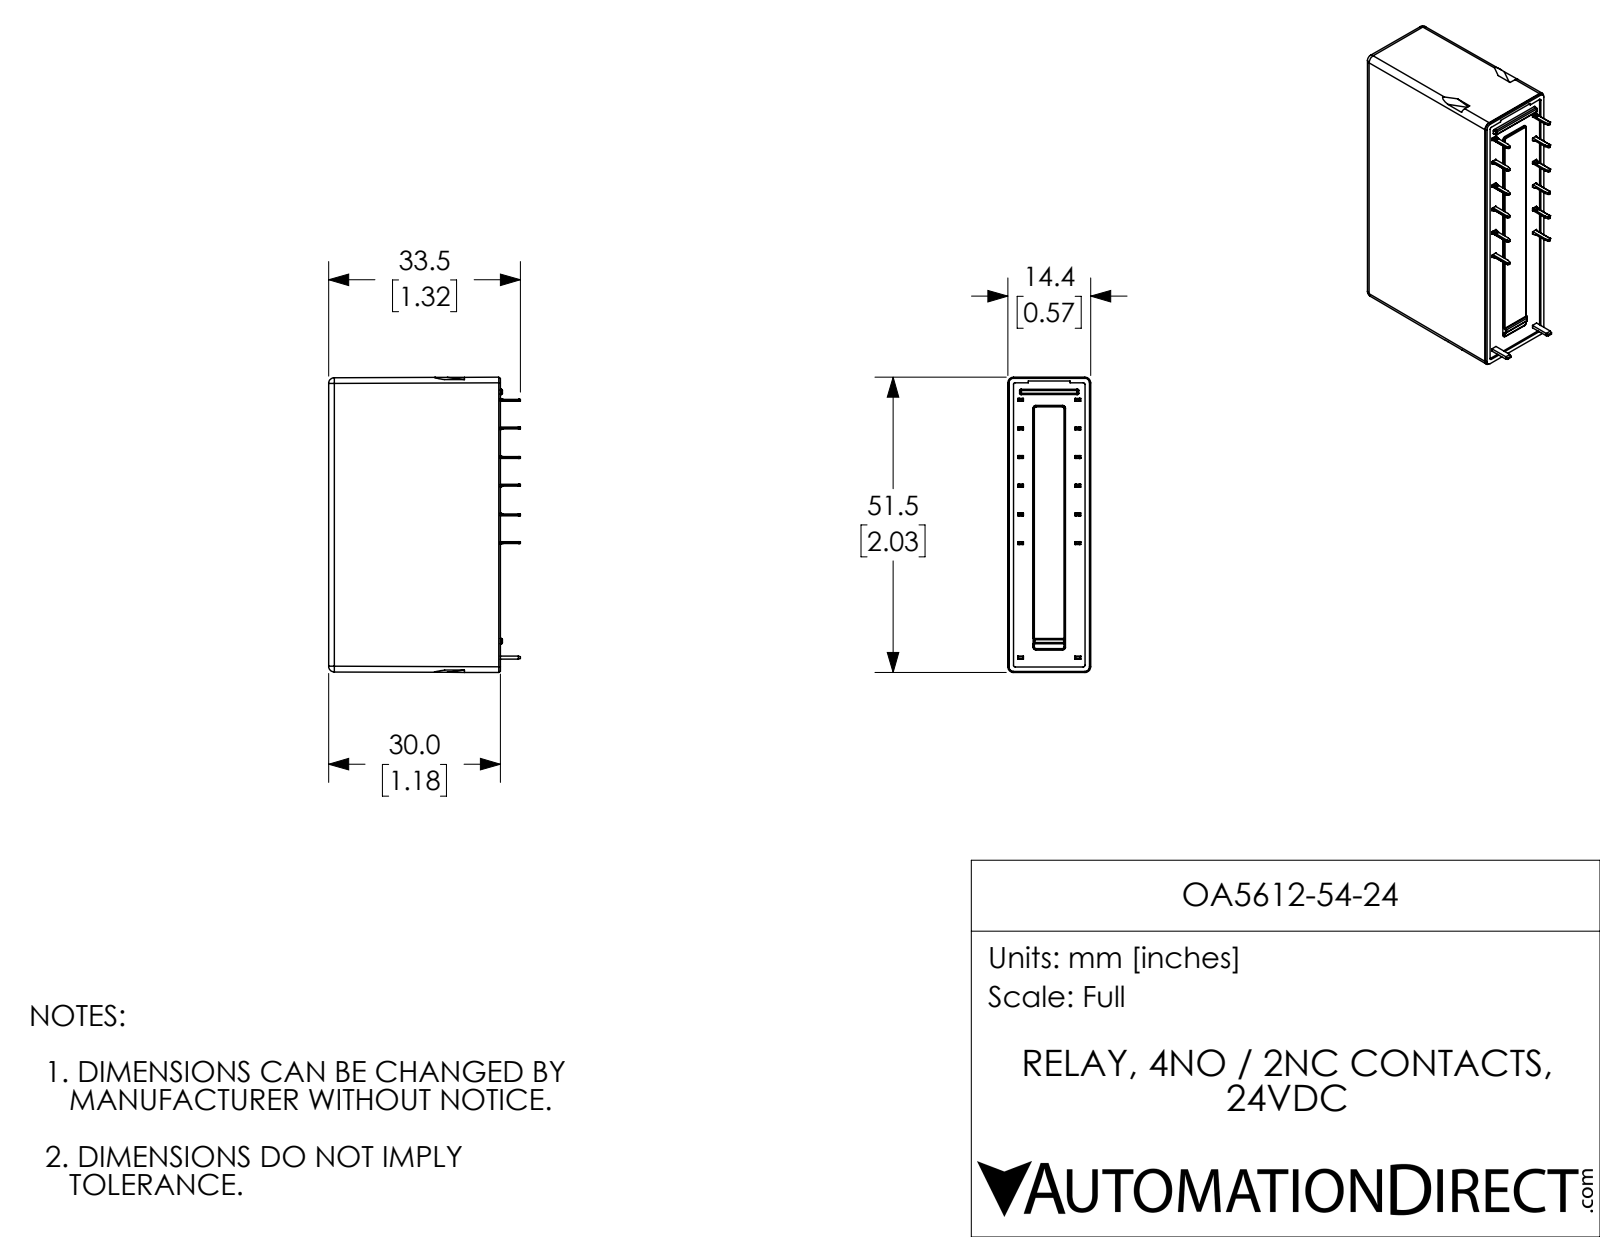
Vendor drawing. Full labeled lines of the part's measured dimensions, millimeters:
Part name (STEP PRODUCT): OA5612-54-24
STEP written by: SolidWorks 2017 (AUTOMOTIVE_DESIGN)
Units: millimetres
Bodies: 1 solid, 434 faces (262 planar, 126 cylindrical, 46 other)
Overall size (bounding box): 51.5 × 33.5 × 14.5
Volume: 21 990 mm³ · Surface area: 5 512 mm²
Round bosses / shafts (diameter × count): ⌀0.8 ×1
Partial cylindrical surfaces — rounded edges, fillets, slot ends (radius × count): R0.2 ×36, R0.2 ×16, R0.5 ×16, R1 ×8, R0.3 ×4, R0.1 ×2, R0.3 ×2
Main face-to-face distances: 29.7, 30, 10, 0.4, 10.8, 4.8, 0.3, 12.5, 1.7, 0.9
